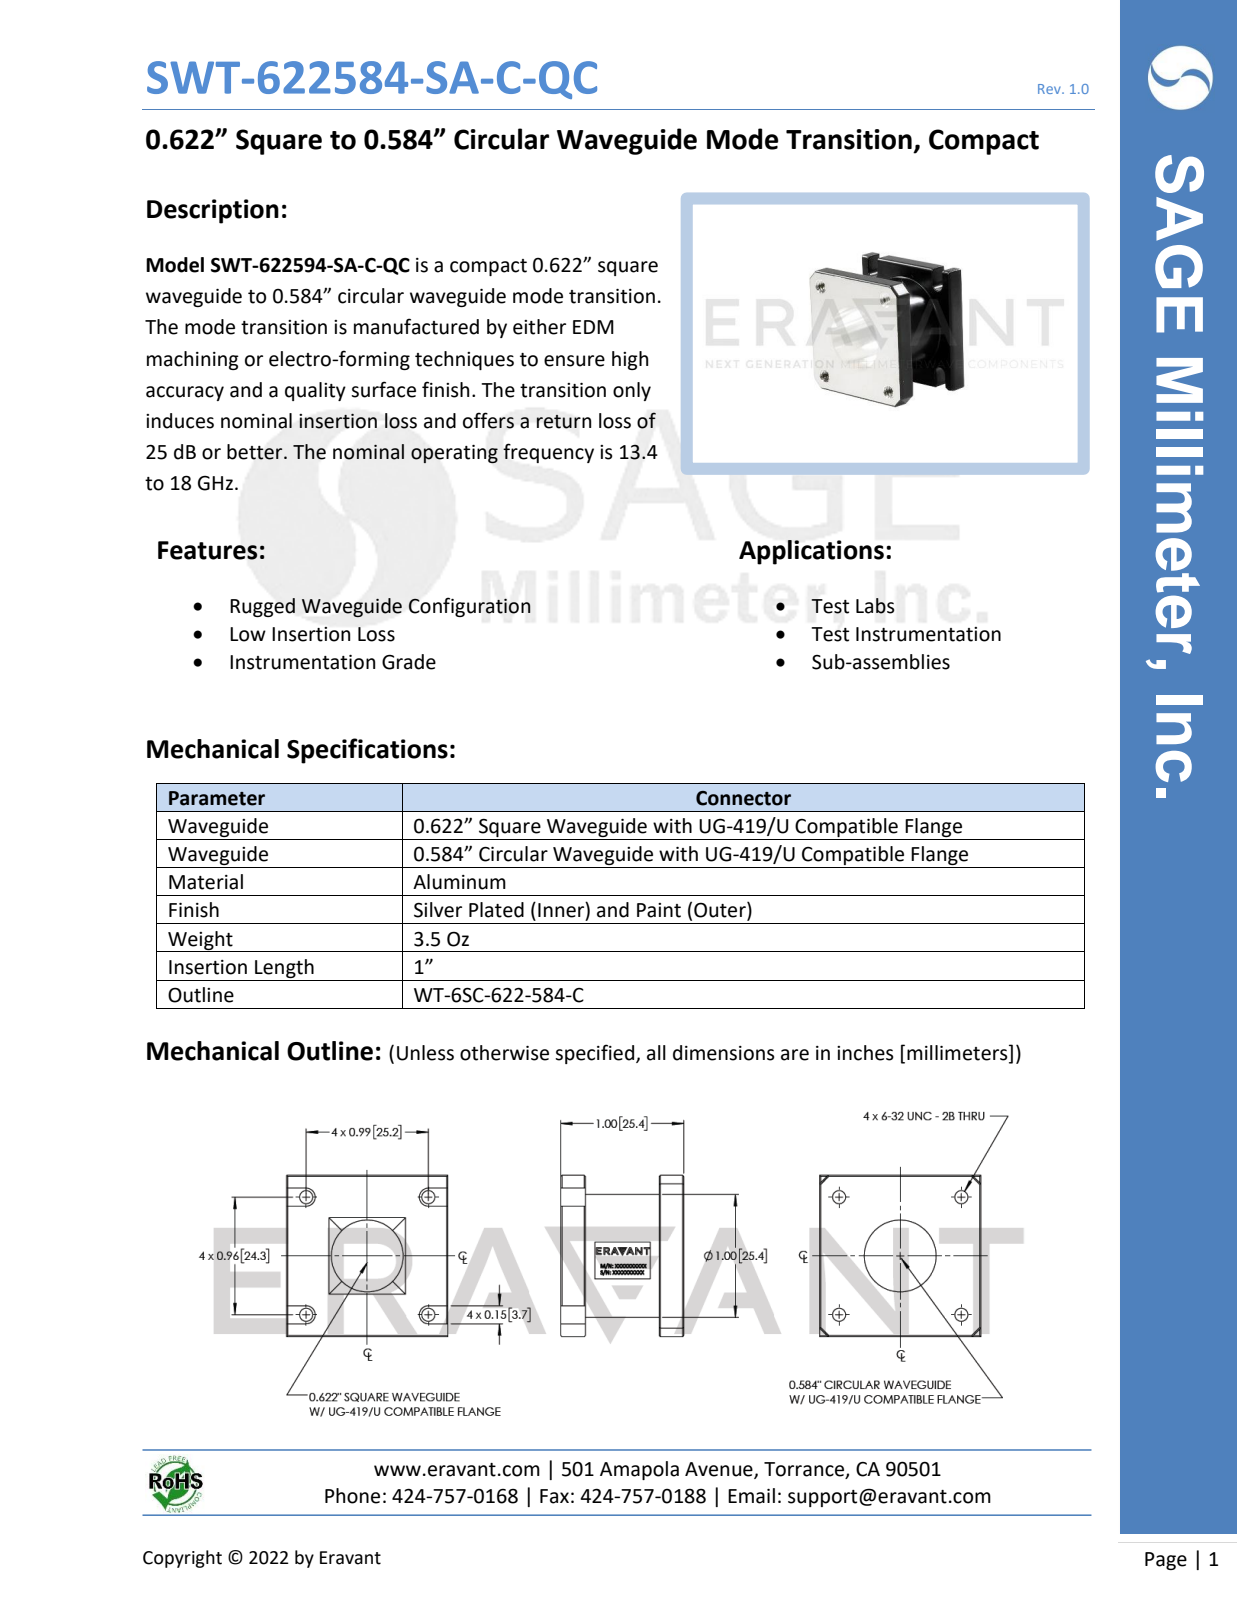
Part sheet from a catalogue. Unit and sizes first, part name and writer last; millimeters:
Units: millimetres
Overall size (bounding box): 33.3 × 33.3 × 25.4
Round holes (diameter × count): ⌀2.7 ×4
Round bosses / shafts (diameter × count): ⌀25.4 ×1
Partial cylindrical surfaces — rounded edges, fillets, slot ends (radius × count): R1.9 ×4
Main face-to-face distances: 5.1, 20.3, 25.4, 33.3, 15.2, 25.1, 4.8, 20.1, 24.9, 2.6
Hole centre spacings: 24.3, 25.2, 35
Volume: 18 320 mm³ · Surface area: 6 089 mm²
Bodies: 1 solid, 84 faces (60 planar, 16 cylindrical, 8 other)
Part name (STEP PRODUCT): WT-6SC-622-584-C
STEP written by: SolidWorks 2021 (AUTOMOTIVE_DESIGN)
